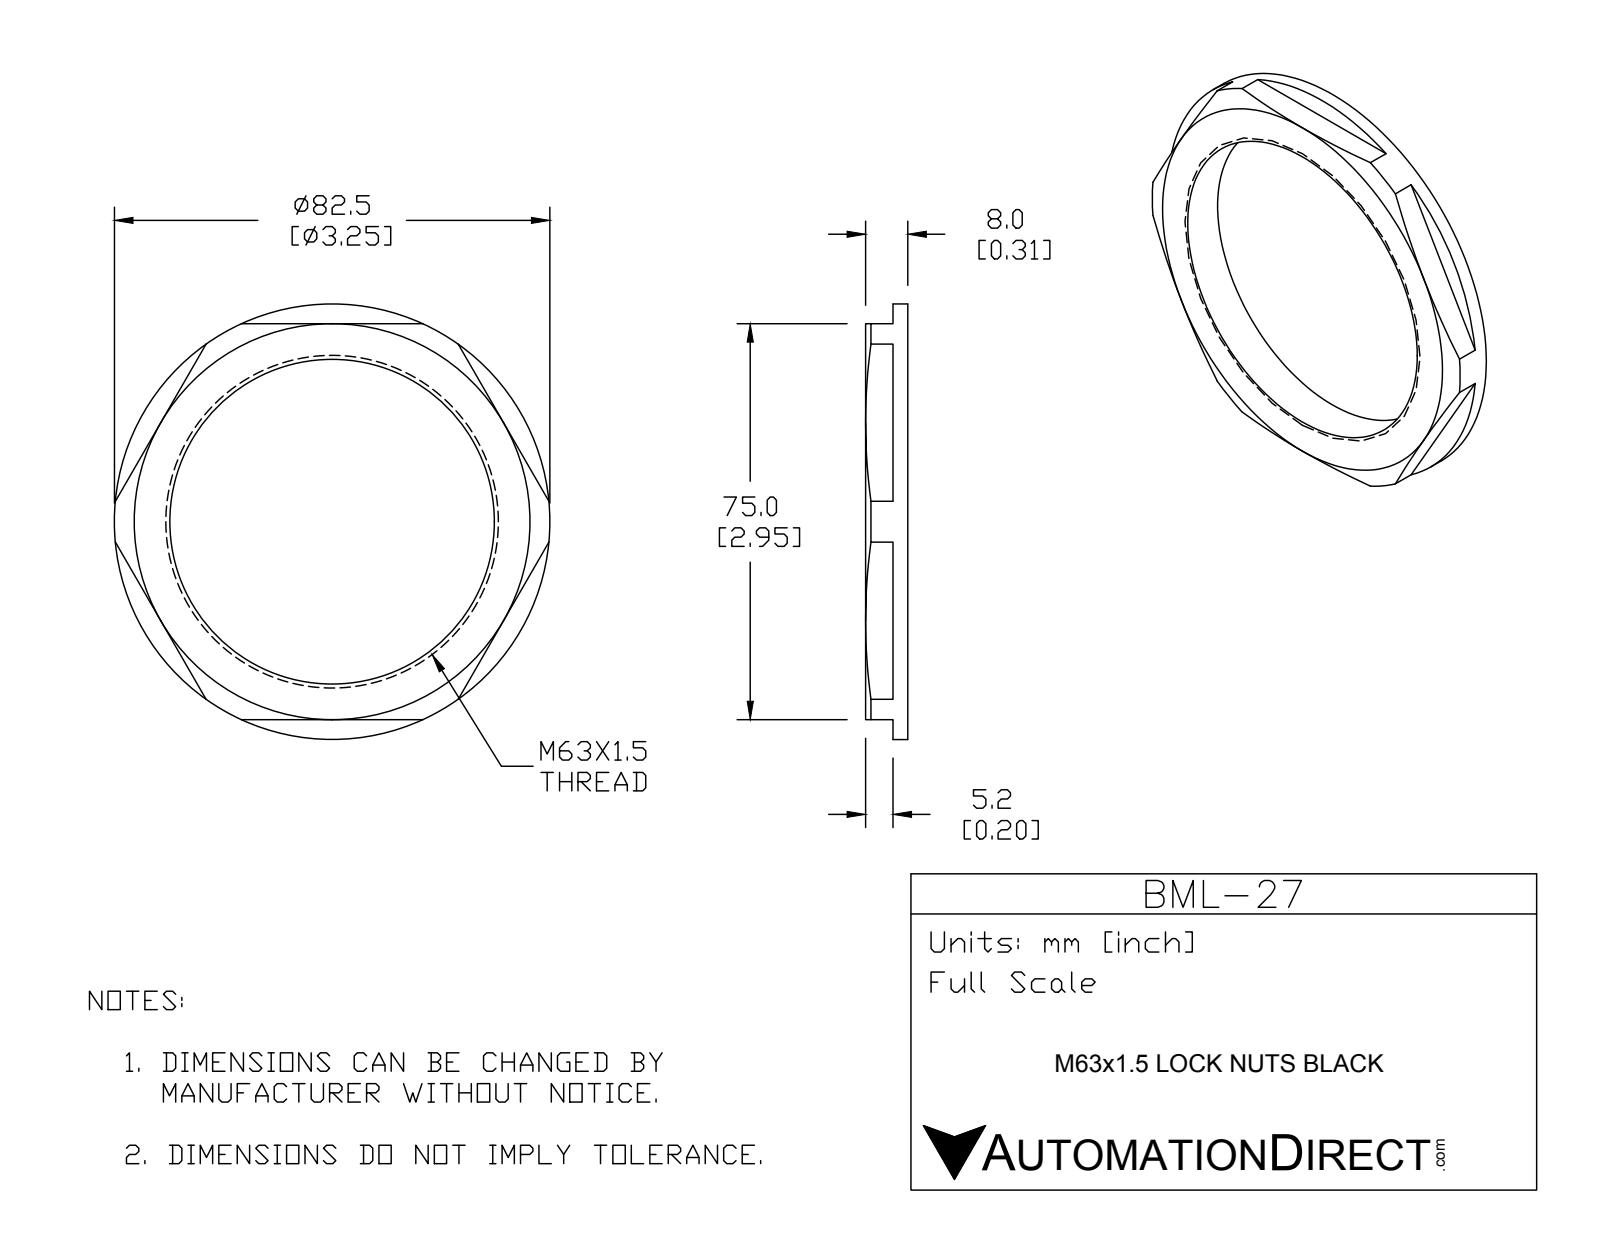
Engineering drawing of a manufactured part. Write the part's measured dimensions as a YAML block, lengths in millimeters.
part_name: "BML-27"
step_written_by: "SolidWorks 2015 (CONFIG_CONTROL_DESIGN)"
units: millimeters
bodies: {solids: 1, faces: 33, planar: 17, cylindrical: 10, other: 6}
overall_size: [82.5, 82.5, 8]
volume: 16135
surface_area: 8237
round_holes:
  - {diameter: 1.5, count: 3}
  - {diameter: 61.5, count: 1}
round_bosses_or_shafts:
  - {diameter: 82.5, count: 1}
face_to_face_distances: [8, 2.8, 5.2, 75, 2.5, 7.7]
hole_center_spacings: [39.8, 68.94]
